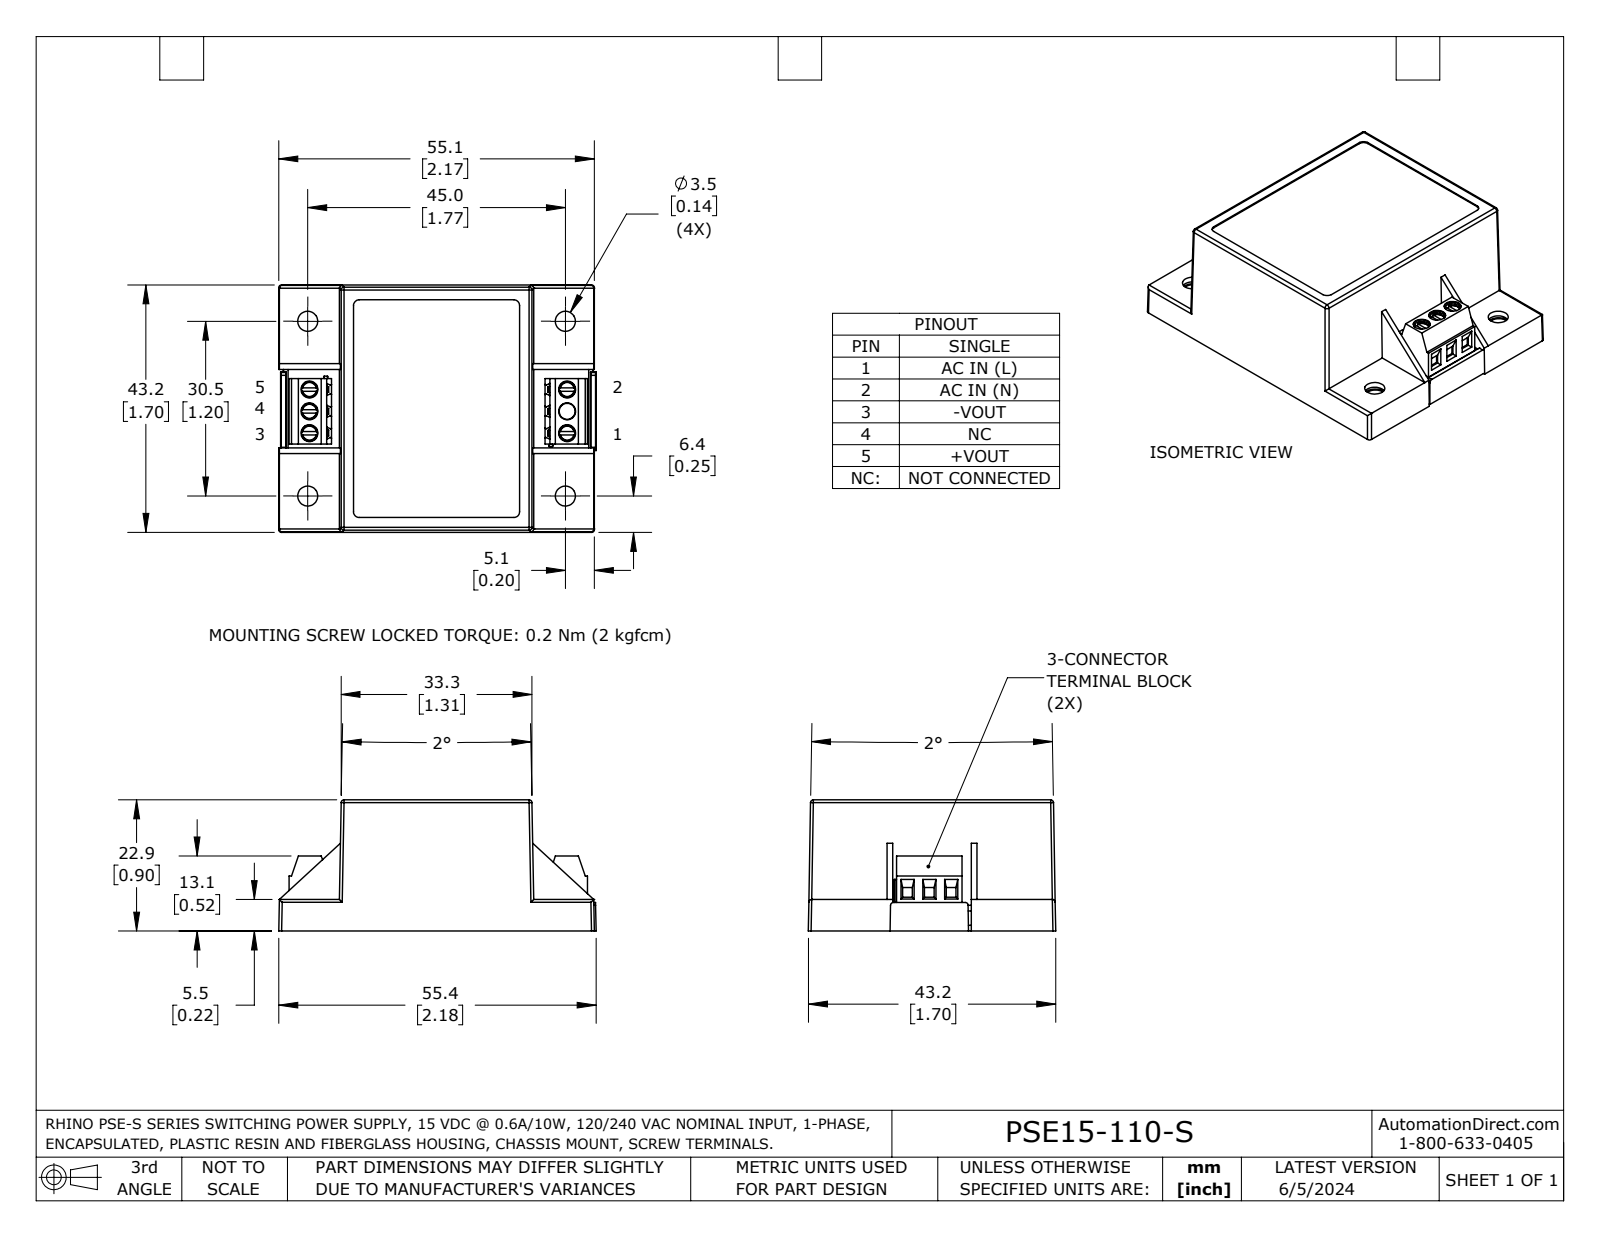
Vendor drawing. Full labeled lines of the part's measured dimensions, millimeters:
Part name (STEP PRODUCT): PSE15-110-S
STEP written by: SolidWorks 2023 (AUTOMOTIVE_DESIGN)
Units: millimetres
Bodies: 5 solids, 655 faces (491 planar, 130 cylindrical, 34 other)
Overall size (bounding box): 50.7 × 43.2 × 43.2
Volume: 10 700 mm³ · Surface area: 22 340 mm²
Round holes (diameter × count): ⌀2.9 ×9, ⌀3.5 ×8, ⌀4.1 ×4, ⌀2.8 ×1
Partial cylindrical surfaces — rounded edges, fillets, slot ends (radius × count): R0.5 ×19, R0.2 ×18, R0.2 ×12, R0.1 ×8, R0.2 ×4, R0.3 ×4, R1 ×4, R2 ×4
Main face-to-face distances: 1, 3.5, 4.5, 18.2, 21.7, 2.5, 17.2, 20.7, 19.2, 22.7
Hole centre spacings: 3.8, 45, 45.2, 11.4, 15.2, 19.1, 7.6, 0.6
